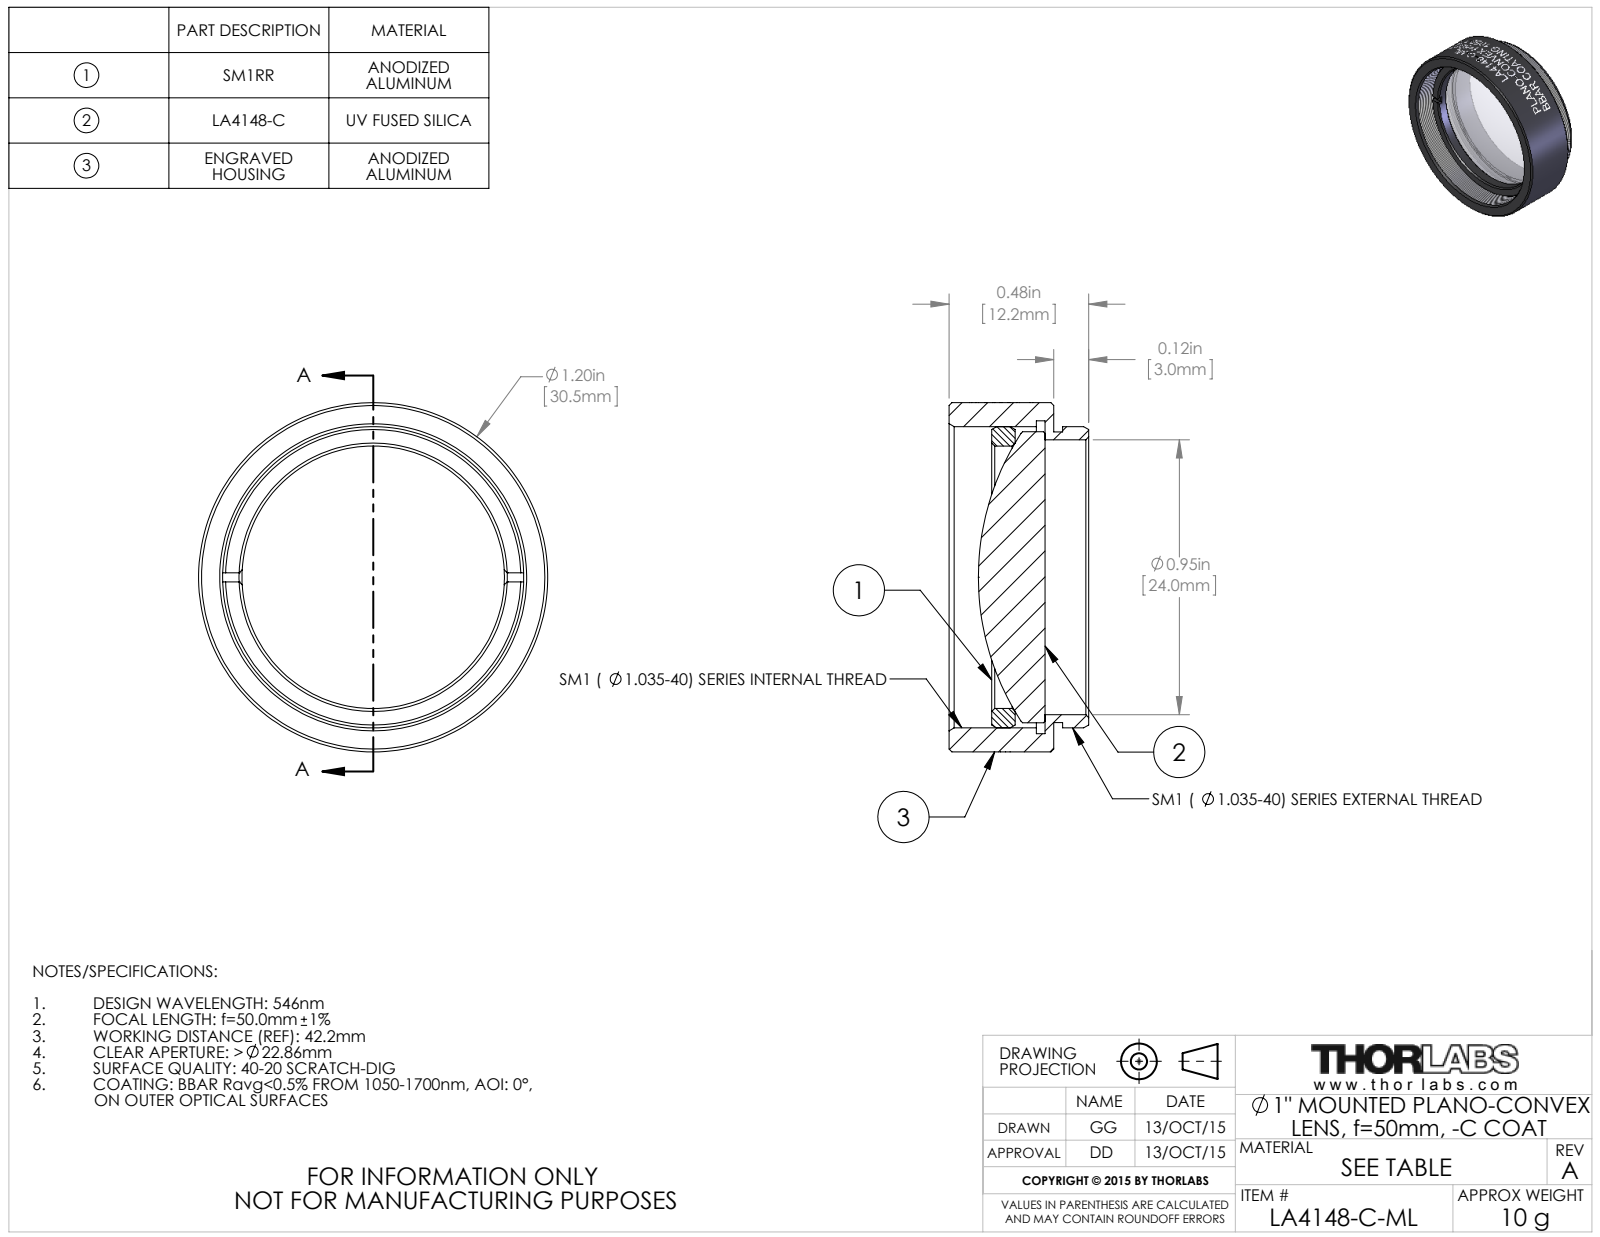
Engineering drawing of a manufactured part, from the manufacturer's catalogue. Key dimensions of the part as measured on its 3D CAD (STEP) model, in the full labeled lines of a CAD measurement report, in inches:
Part name (STEP PRODUCT): TTN039171-E0W
STEP written by: SolidWorks 2014 (CONFIG_CONTROL_DESIGN)
Units: inches
Bodies: 3 solids, 163 faces (20 planar, 115 cylindrical, 28 other)
Overall size (bounding box): 1.2 × 1.2 × 0.48
Volume: 0.258 in³ · Surface area: 6.953 in²
Round holes (diameter × count): ⌀0.902 ×1, ⌀0.945 ×1, ⌀1.035 ×1, ⌀1.075 ×1
Round bosses / shafts (diameter × count): ⌀1.2 ×1, ⌀1.035 ×1, ⌀1 ×1, ⌀0.999 ×1
Main face-to-face distances: 0.03, 0.36, 0.33, 0.133, 0.103, 0.227, 0.213, 0.183, 0.08, 0.147
